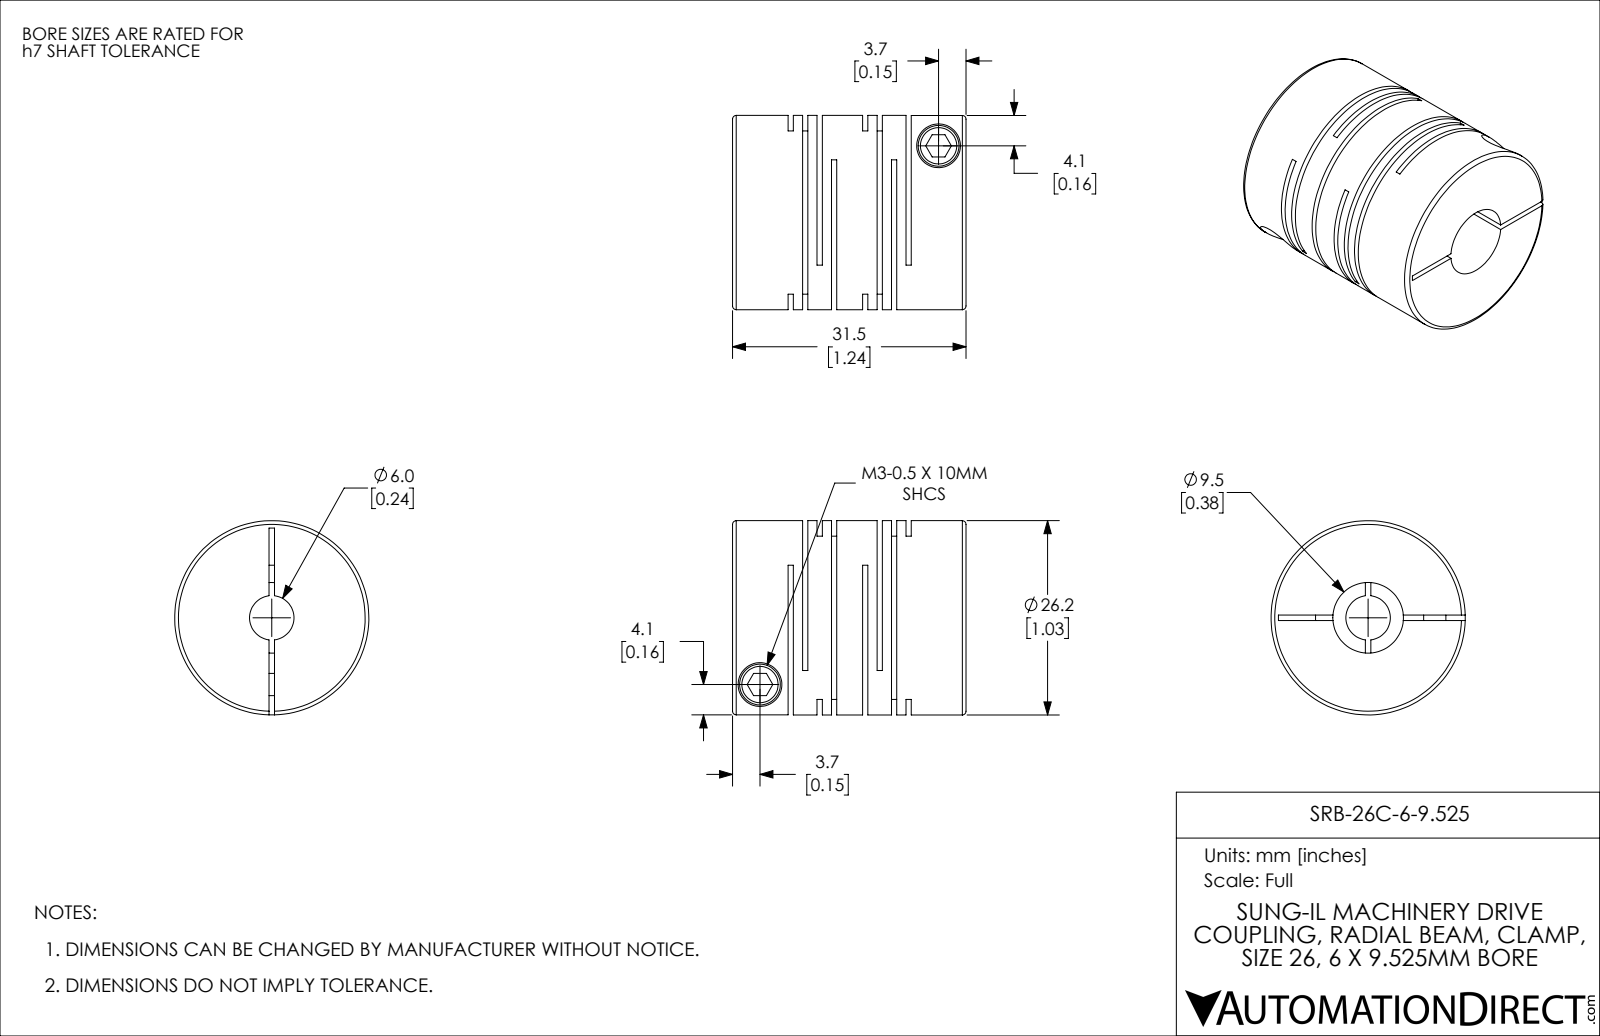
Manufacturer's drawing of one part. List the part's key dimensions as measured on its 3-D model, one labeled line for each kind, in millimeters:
Part name (STEP PRODUCT): SRB-26C-6-9.525
STEP written by: SolidWorks 2021 (CONFIG_CONTROL_DESIGN)
Units: millimetres
Bodies: 1 solid, 114 faces (60 planar, 42 cylindrical, 12 other)
Overall size (bounding box): 31.5 × 26.2 × 26.2
Volume: 12 428 mm³ · Surface area: 10 881 mm²
Round holes (diameter × count): ⌀3 ×2, ⌀5.9 ×2, ⌀6 ×1, ⌀9.53 ×1
Round bosses / shafts (diameter × count): ⌀5.5 ×2, ⌀26.2 ×1
Main face-to-face distances: 1.95, 10.05, 0.71, 3.9, 8.1, 12, 1.24, 2.66, 9.34, 13.95
